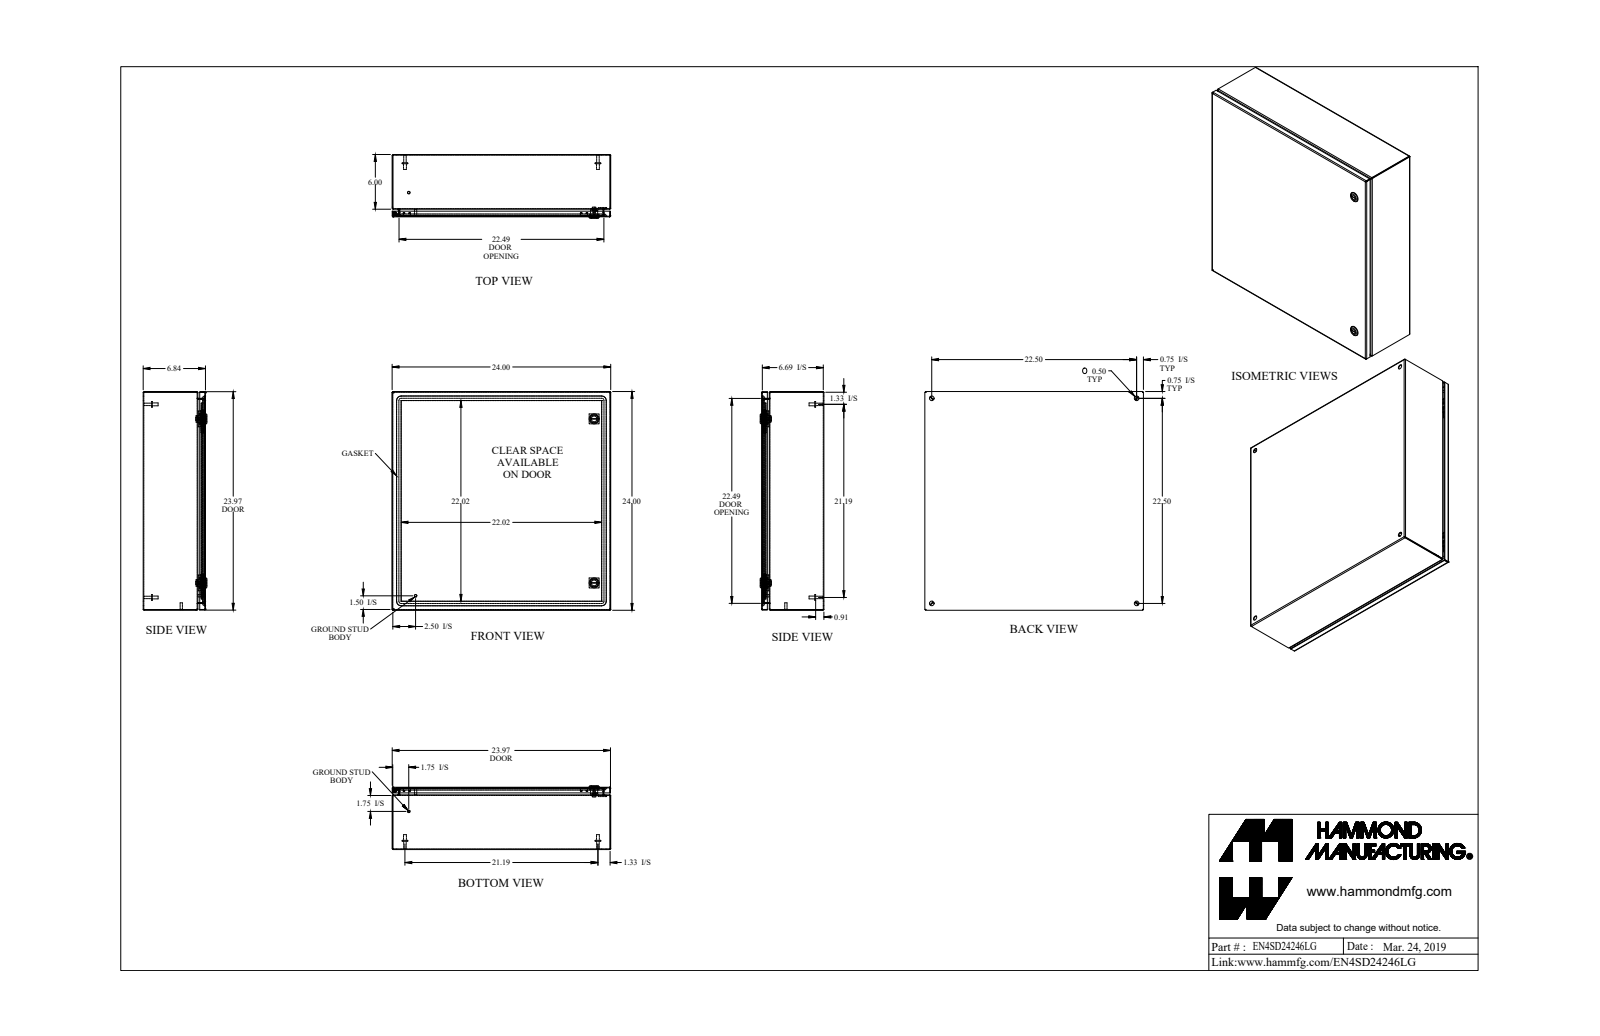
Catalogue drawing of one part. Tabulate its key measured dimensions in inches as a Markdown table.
| quantity | value |
| --- | --- |
| part name | EN4SD24246LG_Default |
| STEP written by | SolidWorks 2019 (CONFIG_CONTROL_DESIGN) |
| units | inches |
| bodies | 27 solids, 783 faces (386 planar, 257 cylindrical, 140 other) |
| overall size | 24 × 24 × 6.997 |
| volume | 150.2 in³ |
| surface area | 4 207 in² |
| round holes (diameter × count) | 0.5 × 4, 0.232 × 2, 0.625 × 2, 0.785 × 2, 0.172 × 1, 0.24 × 1, 0.242 × 1 |
| round bosses / shafts (diameter × count) | 0.625 × 4, 0.313 × 4, 0.27 × 4, 1.1 × 2, 0.525 × 2, 0.281 × 2, 0.25 × 2, 0.455 × 1 |
| partial cylindrical surfaces (radius × count) | 0.036 × 20, 0.108 × 20, 0.043 × 12, 0.081 × 12, 0.382 × 12, 19.003 × 8, 0.006 × 4, 0.062 × 4 |
| main face-to-face distances | 0.072, 6.765, 6.693, 6.837, 23.928, 23.856, 24, 0.837, 5.928, 0.75 |
| hole center spacings | 22.5, 31.82, 2.493, 2.494, 17.999, 20.277, 20.278, 21.545 |
